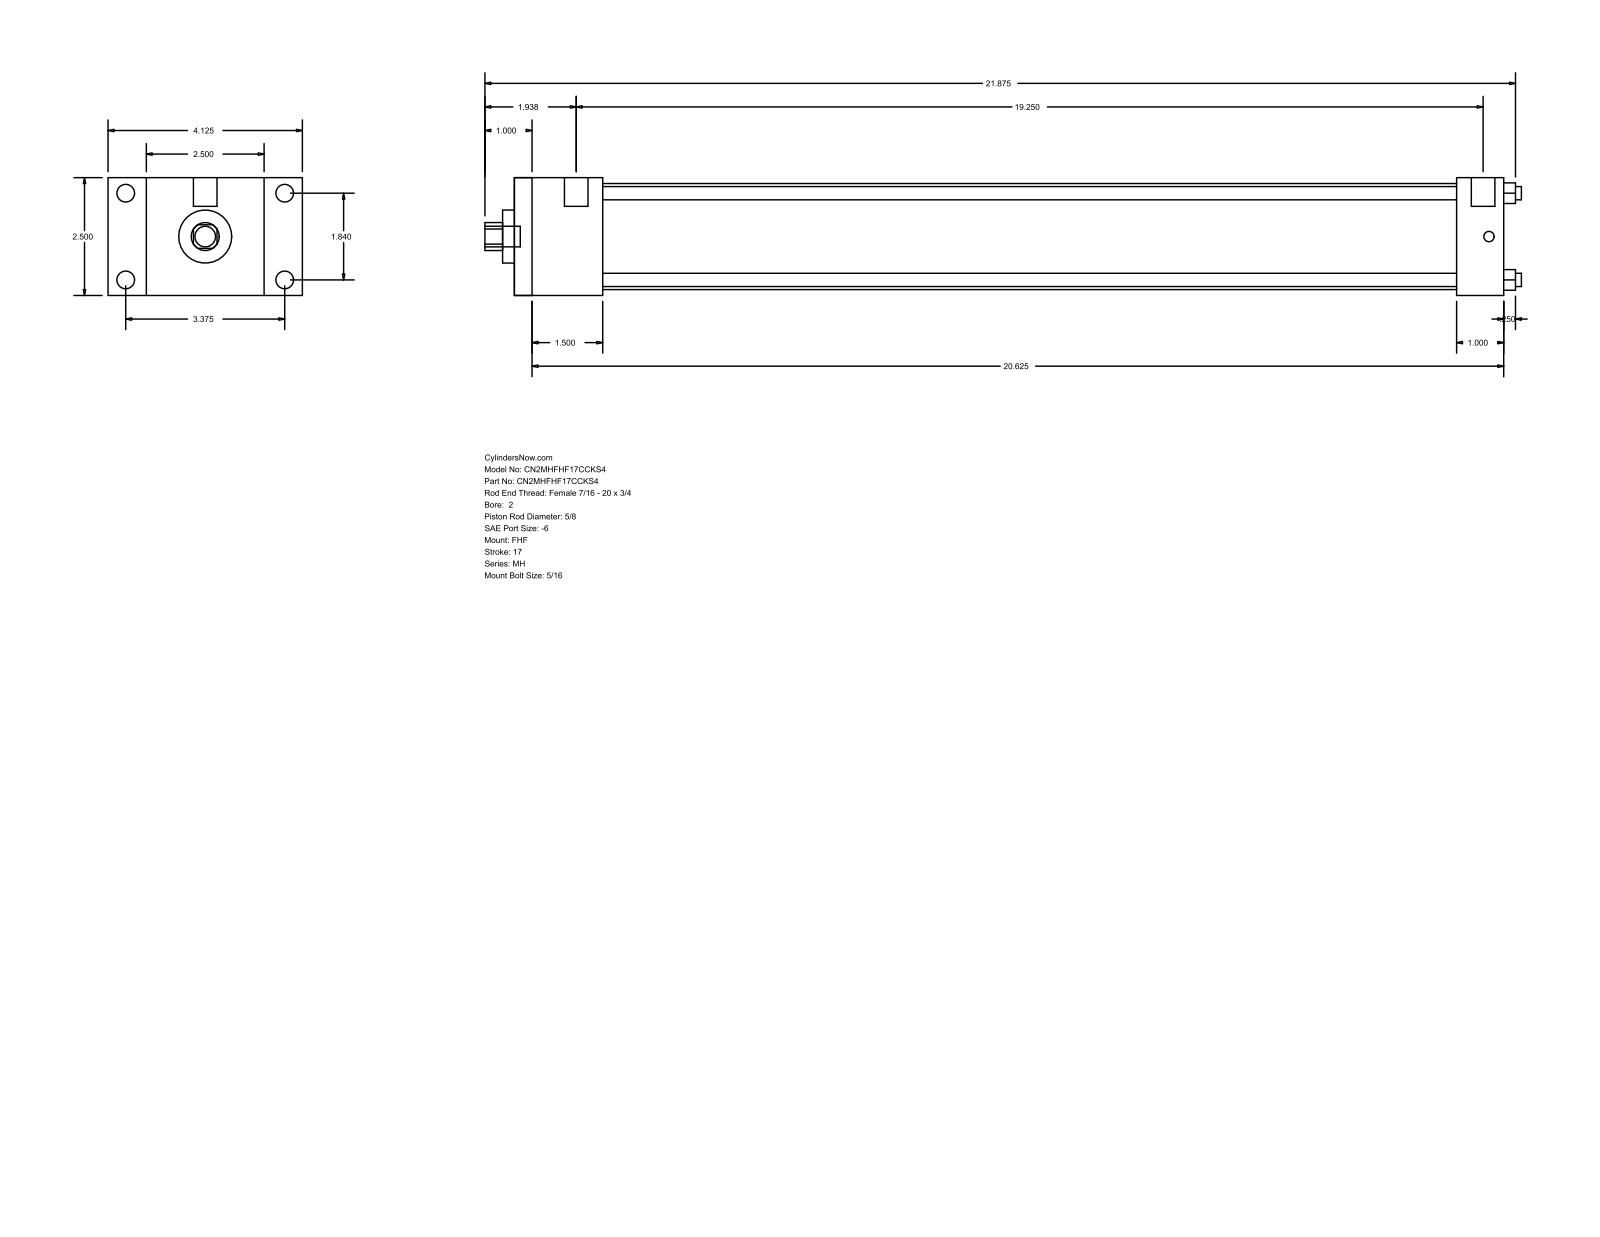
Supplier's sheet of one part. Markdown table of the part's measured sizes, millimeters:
| quantity | value |
| --- | --- |
| part name | MH_FHF__0200_0.625 |
| STEP written by | GSSL Pune (CONFIG_CONTROL_DESIGN) |
| units | millimeters |
| bodies | 0 solids, 88 faces (60 planar, 28 cylindrical, 0 other) |
| overall size | 558.8 × 104.78 × 63.5 |
| round holes (diameter × count) | 7.14 × 4, 15.88 × 1, 28.57 × 1, 57.15 × 1 |
| round bosses / shafts (diameter × count) | 9.53 × 4, 5.56 × 4, 12.7 × 2, 11.11 × 1 |
| partial cylindrical surfaces (radius × count) | 7.54 × 1 |
| main face-to-face distances | 63.5, 47.62, 533.39, 485.77, 20.64, 84.14, 104.78, 508, 460.38, 25.39 |
| hole center spacings | 33.05, 46.74, 66.1 |
